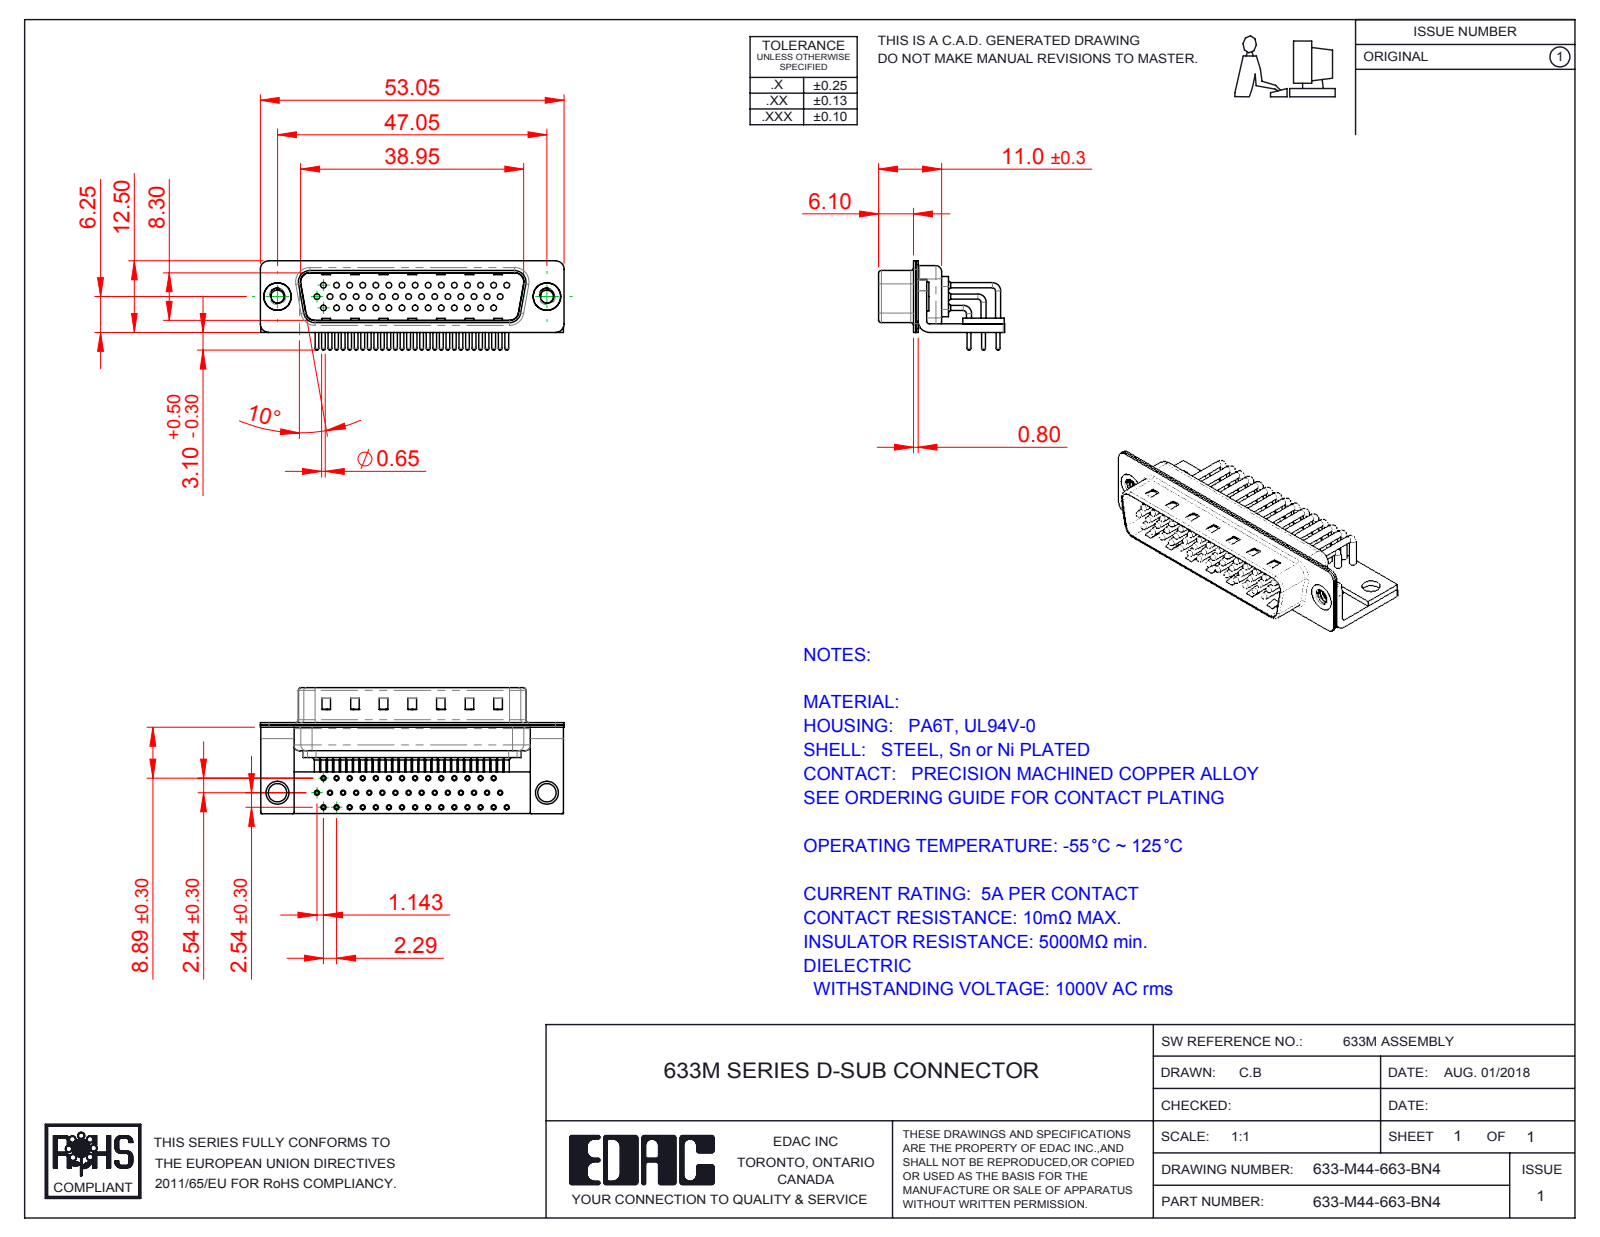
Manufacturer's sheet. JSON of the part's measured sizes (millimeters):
{"part_name": "633M Contact Row 3; 633M Contact Row 2; 633M Contact Row 1; 633M Shell Front_44 Contacts (+6 more)", "step_written_by": "SolidWorks 2016 (CONFIG_CONTROL_DESIGN)", "units": "millimeters", "bodies": {"solids": 52, "faces": 5354, "planar": 3013, "cylindrical": 1831, "other": 510}, "overall_size": [53.05, 22, 15.6], "volume_mm3": 3754, "surface_area_mm2": 11606, "round_holes": [[0.9, 44], [1, 44], [1.7, 44], [2, 44], [2.26, 2], [3.2, 2], [4, 2], [4.8, 2]], "round_bosses_or_shafts": [[0.9, 45], [1.5, 44], [0.65, 44], [5, 2], [4.9, 2], [1, 2]], "partial_cylinders_radius": [[1.01, 44], [0.25, 16], [1.5, 16], [2, 13], [0.5, 9], [1.6, 8], [0.6, 4], [0.65, 4]], "face_to_face_distances": [0.4, 0.85, 1.5, 1.25, 1, 1.9, 0.8, 9.55, 10.4, 8.3], "hole_center_spacings": [2.28, 2.29, 4.57, 6.86, 3.96, 11.43, 8.24, 16]}
